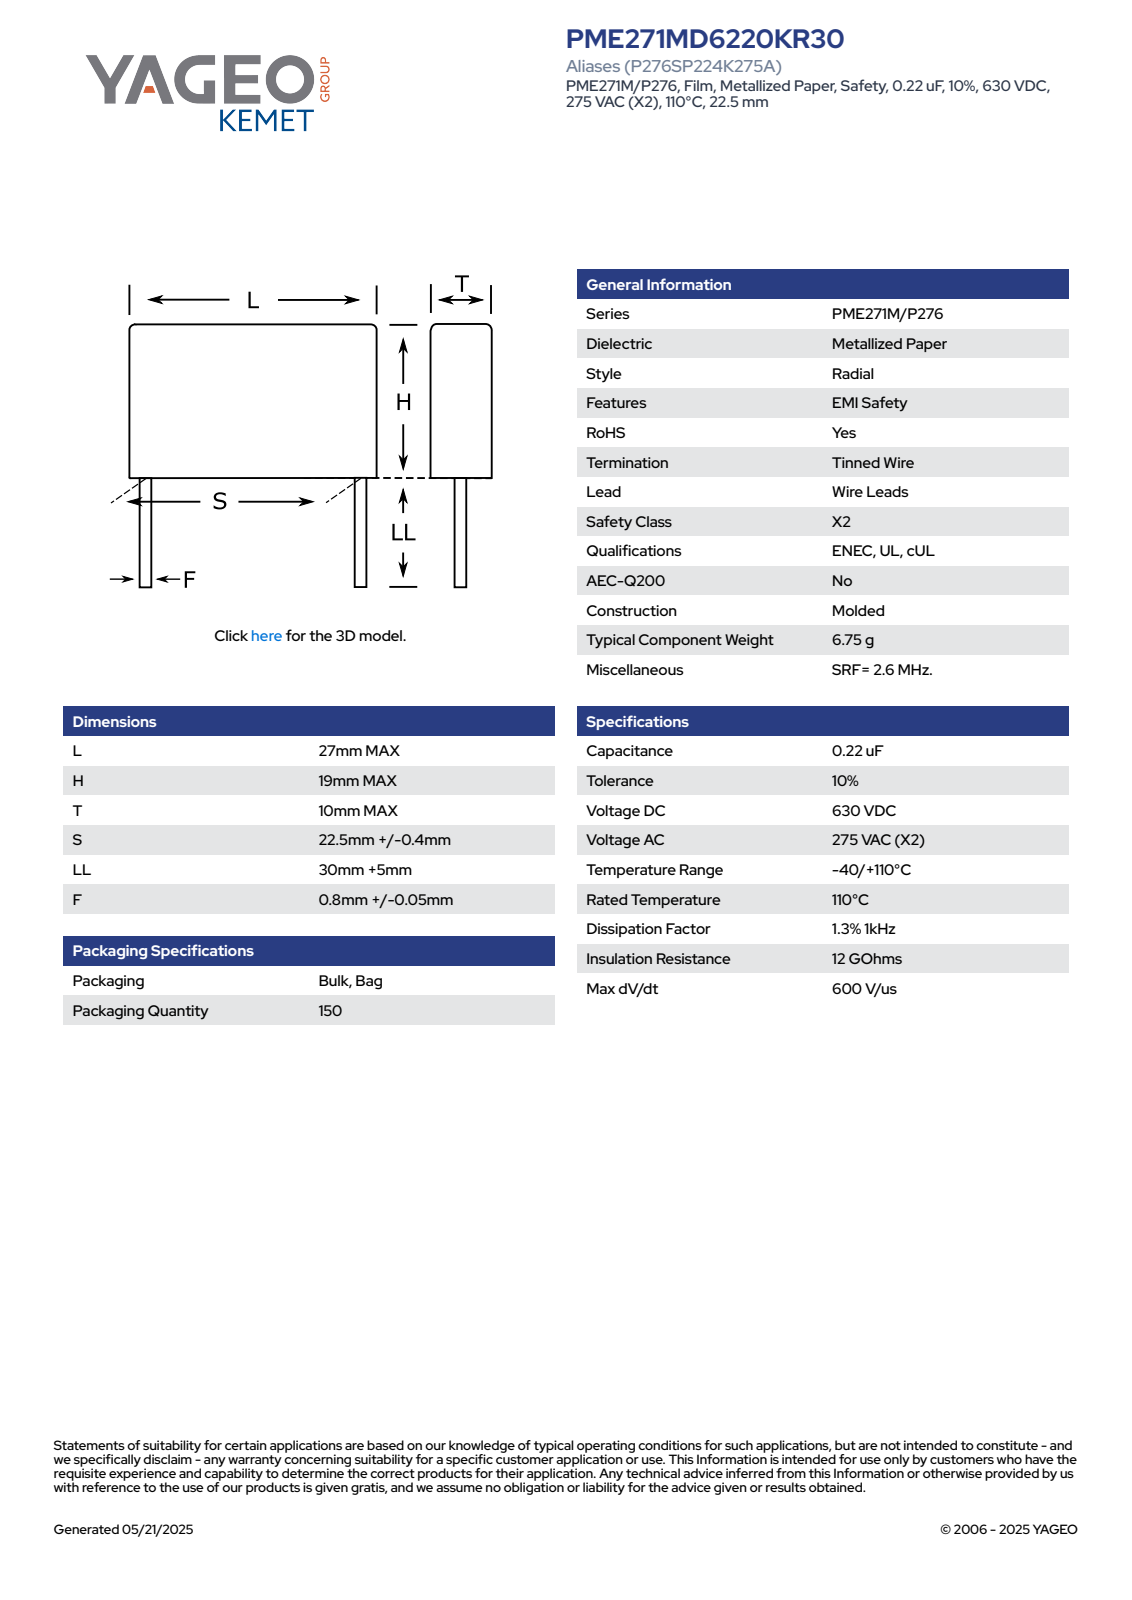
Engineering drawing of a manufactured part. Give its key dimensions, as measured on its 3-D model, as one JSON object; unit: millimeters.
{"part_name": "CFR_MOLDED_27X19X10_L27H19T10S22.5LL35F0.8", "step_written_by": "SolidWorks 2014 (AUTOMOTIVE_DESIGN)", "units": "millimeters", "bodies": {"solids": 4, "faces": 73, "planar": 65, "cylindrical": 8, "other": 0}, "overall_size": [54, 27, 10.01], "volume_mm3": 5161, "surface_area_mm2": 2141, "round_bosses_or_shafts": [[0.8, 2]], "partial_cylinders_radius": [[0.5, 4]], "face_to_face_distances": [10, 19, 27, 10.01, 35, 54, 45.39, 10.39, 8.61, 42.97]}
